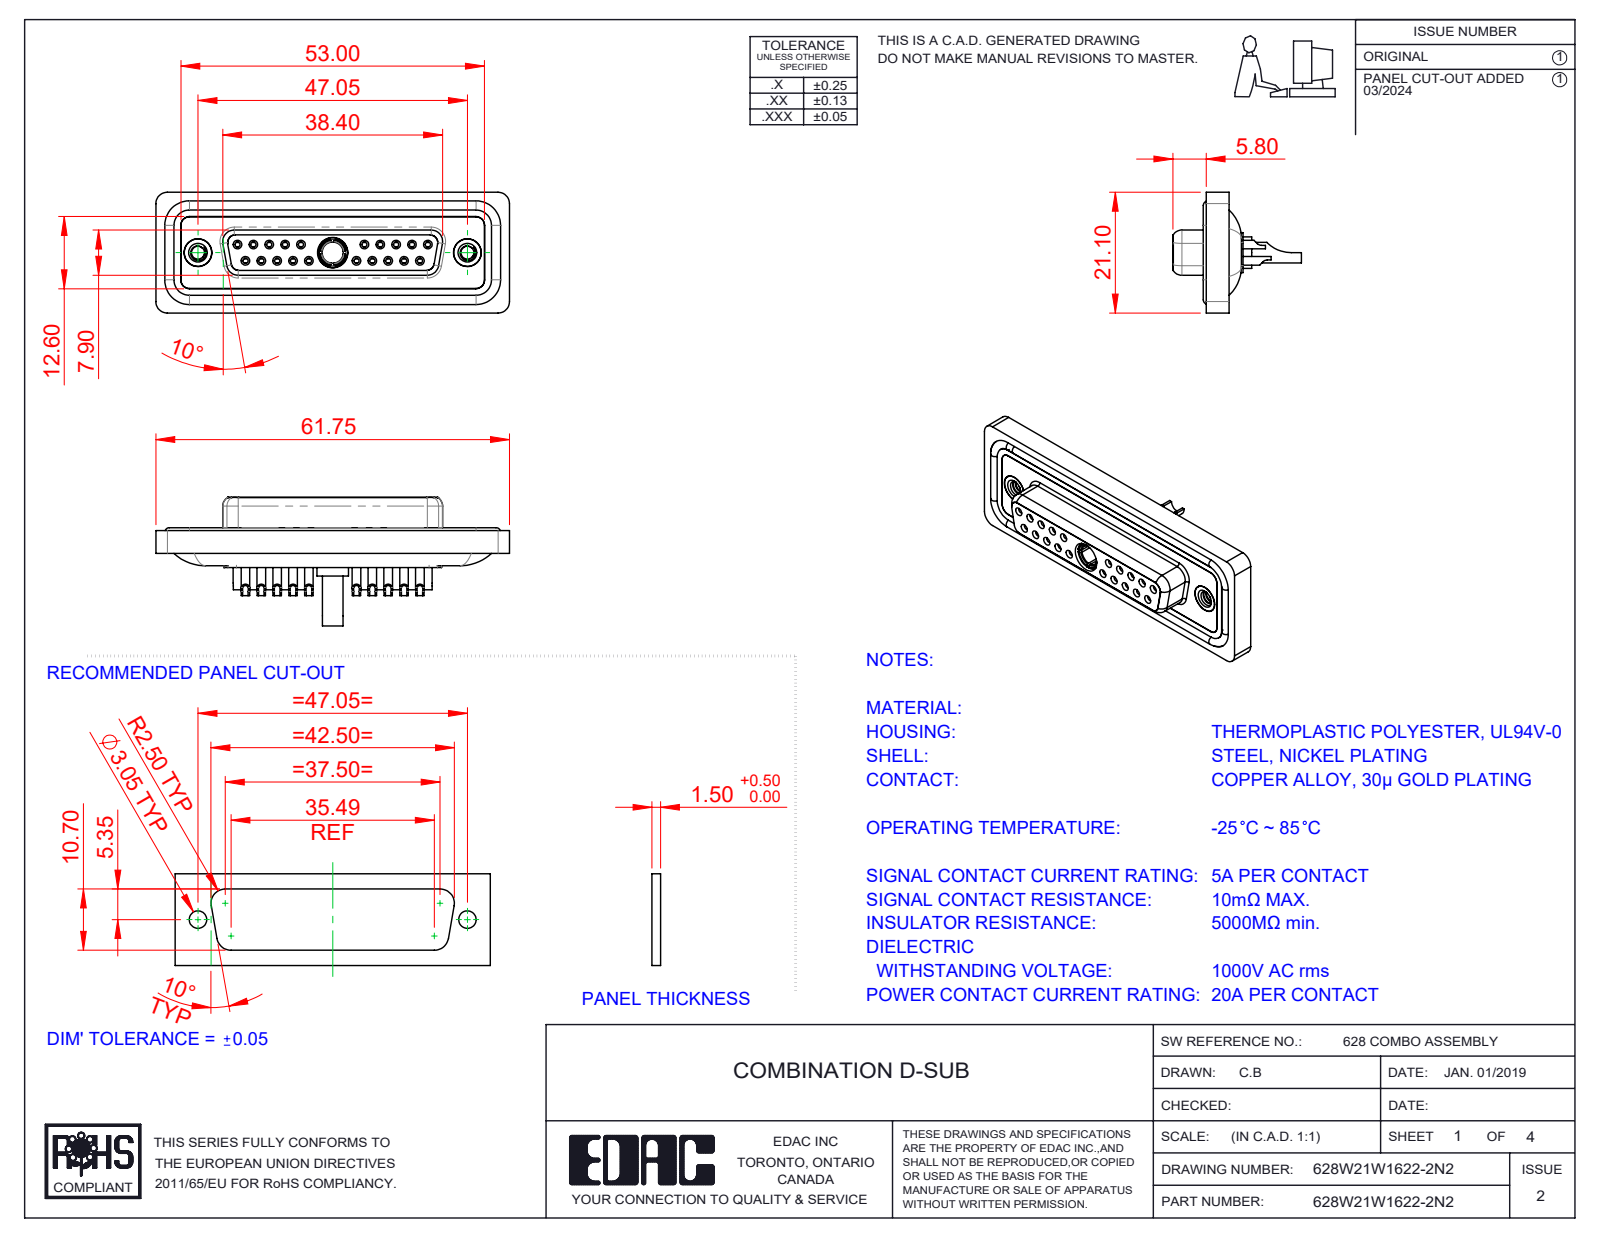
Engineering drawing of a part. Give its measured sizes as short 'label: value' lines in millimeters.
name: Power Socket_20A SC; 628Combo Contact Row 1_22; 628W21W1622-2N2; 628Combo Shell Front_25 Contacts (+5 more)
written by: SolidWorks 2023 (CONFIG_CONTROL_DESIGN)
unit: mm
bodies: 29 solids, 1566 faces (477 planar, 634 cylindrical, 455 other)
size: 61.75 × 22.45 × 21.1
volume: 8 427 mm³; area: 14 294 mm²
holes: 20× ⌀0.9, 20× ⌀1, 20× ⌀1.1, 20× ⌀1.5, 20× ⌀2, 10× ⌀1.6, 10× ⌀1.7, 3× ⌀4.85, 2× ⌀2.26, 2× ⌀4, 2× ⌀4.05, 2× ⌀5
bosses: 20× ⌀2.2, 14× ⌀1.6, 2× ⌀4.95, 2× ⌀4.8, 1× ⌀5.5, 1× ⌀5.2, 1× ⌀4.96, 1× ⌀4.75
rounds: 22× R1.5, 18× R2, 8× R1.35, 8× R1.6, 6× R1, 4× R0.25, 4× R0.5, 4× R0.6
face distances: 0.4, 1.8, 7.45, 5.65, 6.6, 0.5, 1.6, 7.05, 2.9, 1.1
hole spacings: 3.16, 2.77, 5.54, 5.03, 8.31, 7.48, 16.62, 19.39
